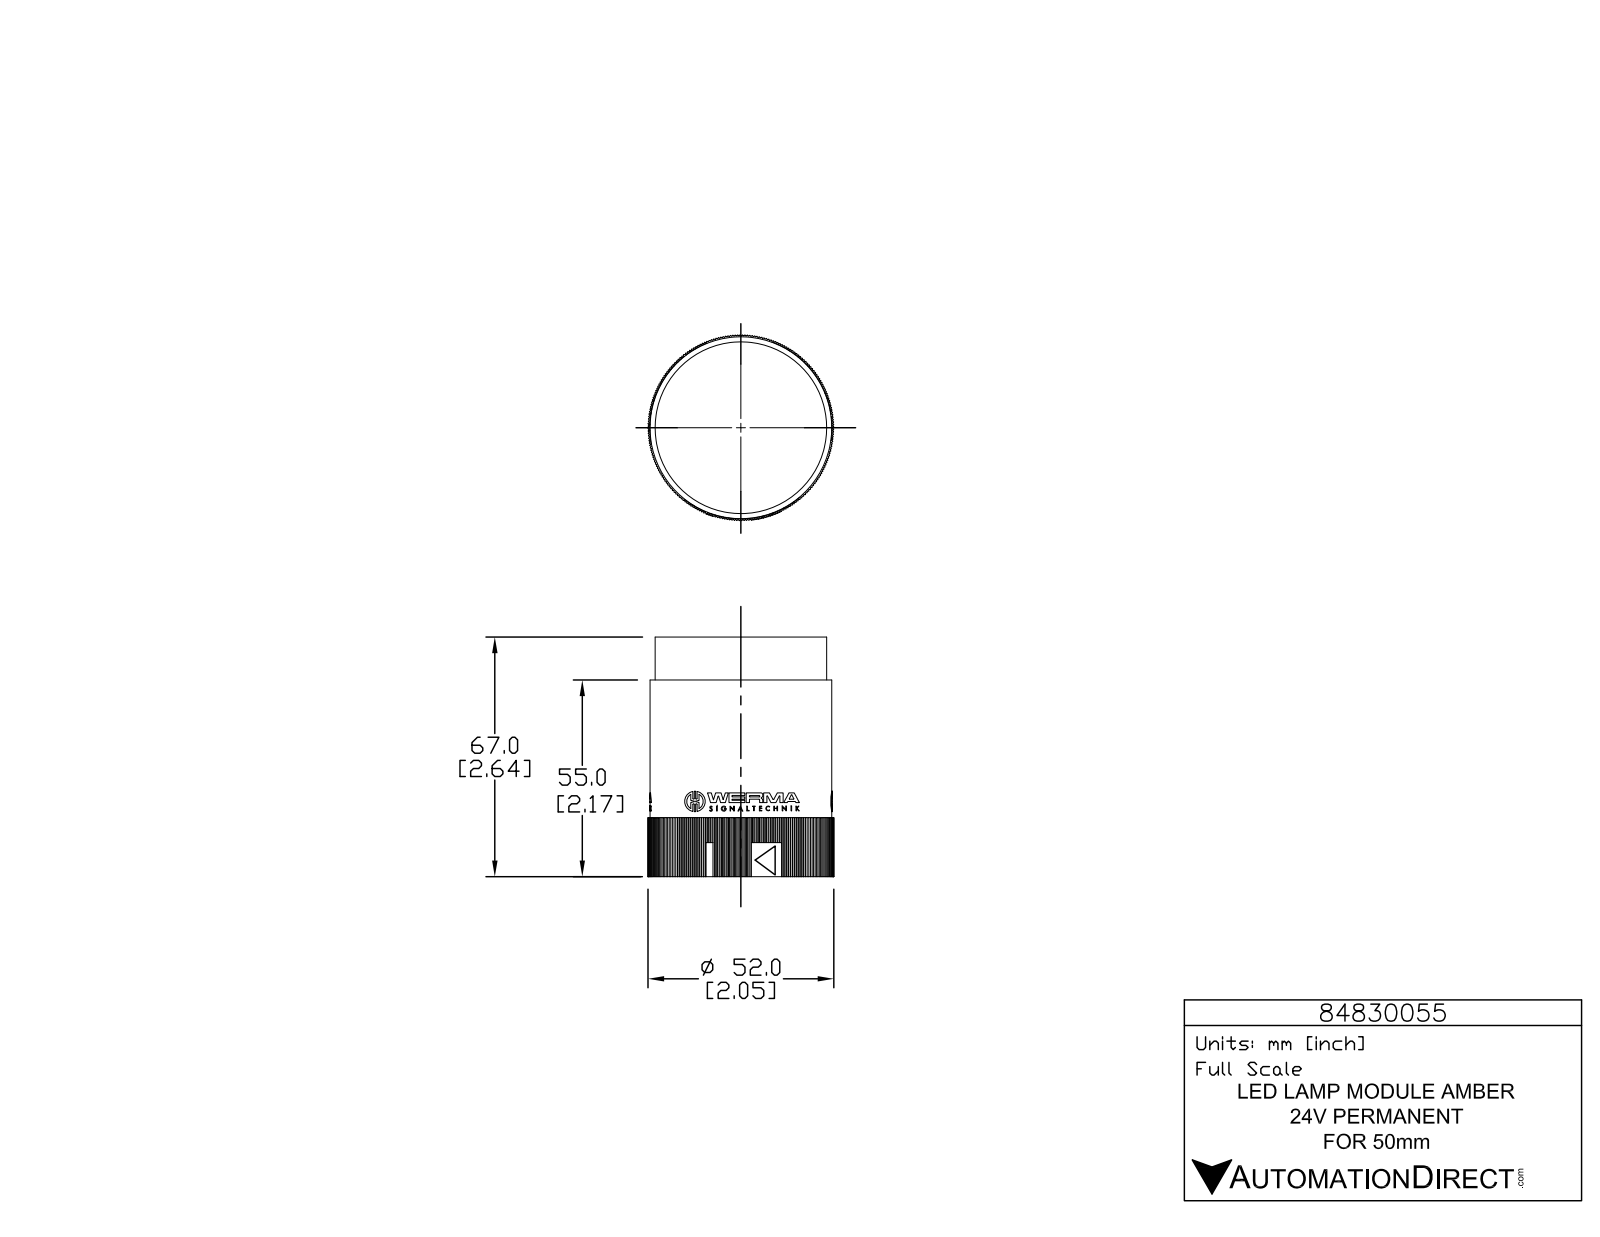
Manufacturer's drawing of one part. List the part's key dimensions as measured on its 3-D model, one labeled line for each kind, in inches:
Part name (STEP PRODUCT): 84830055
STEP written by: SolidWorks 2015 (AUTOMOTIVE_DESIGN)
Units: inches
Bodies: 1 solid, 1265 faces (1020 planar, 245 cylindrical, 0 other)
Overall size (bounding box): 2.638 × 2.047 × 2.047
Volume: 6.873 in³ · Surface area: 27.62 in²
Round holes (diameter × count): ⌀0.039 ×3, ⌀1.898 ×1
Round bosses / shafts (diameter × count): ⌀0.226 ×3, ⌀0.056 ×3, ⌀2.002 ×1, ⌀1.89 ×1
Partial cylindrical surfaces — rounded edges, fillets, slot ends (radius × count): R0.008 ×6, R0.008 ×6, R0.008 ×6, R0.131 ×6, R0.004 ×3, R0.005 ×3, R0.008 ×3, R0.008 ×3
Main face-to-face distances: 2.165, 1.428, 1.429, 1.429, 0.472, 2.638, 1.428, 1.428, 1.693, 1.988
